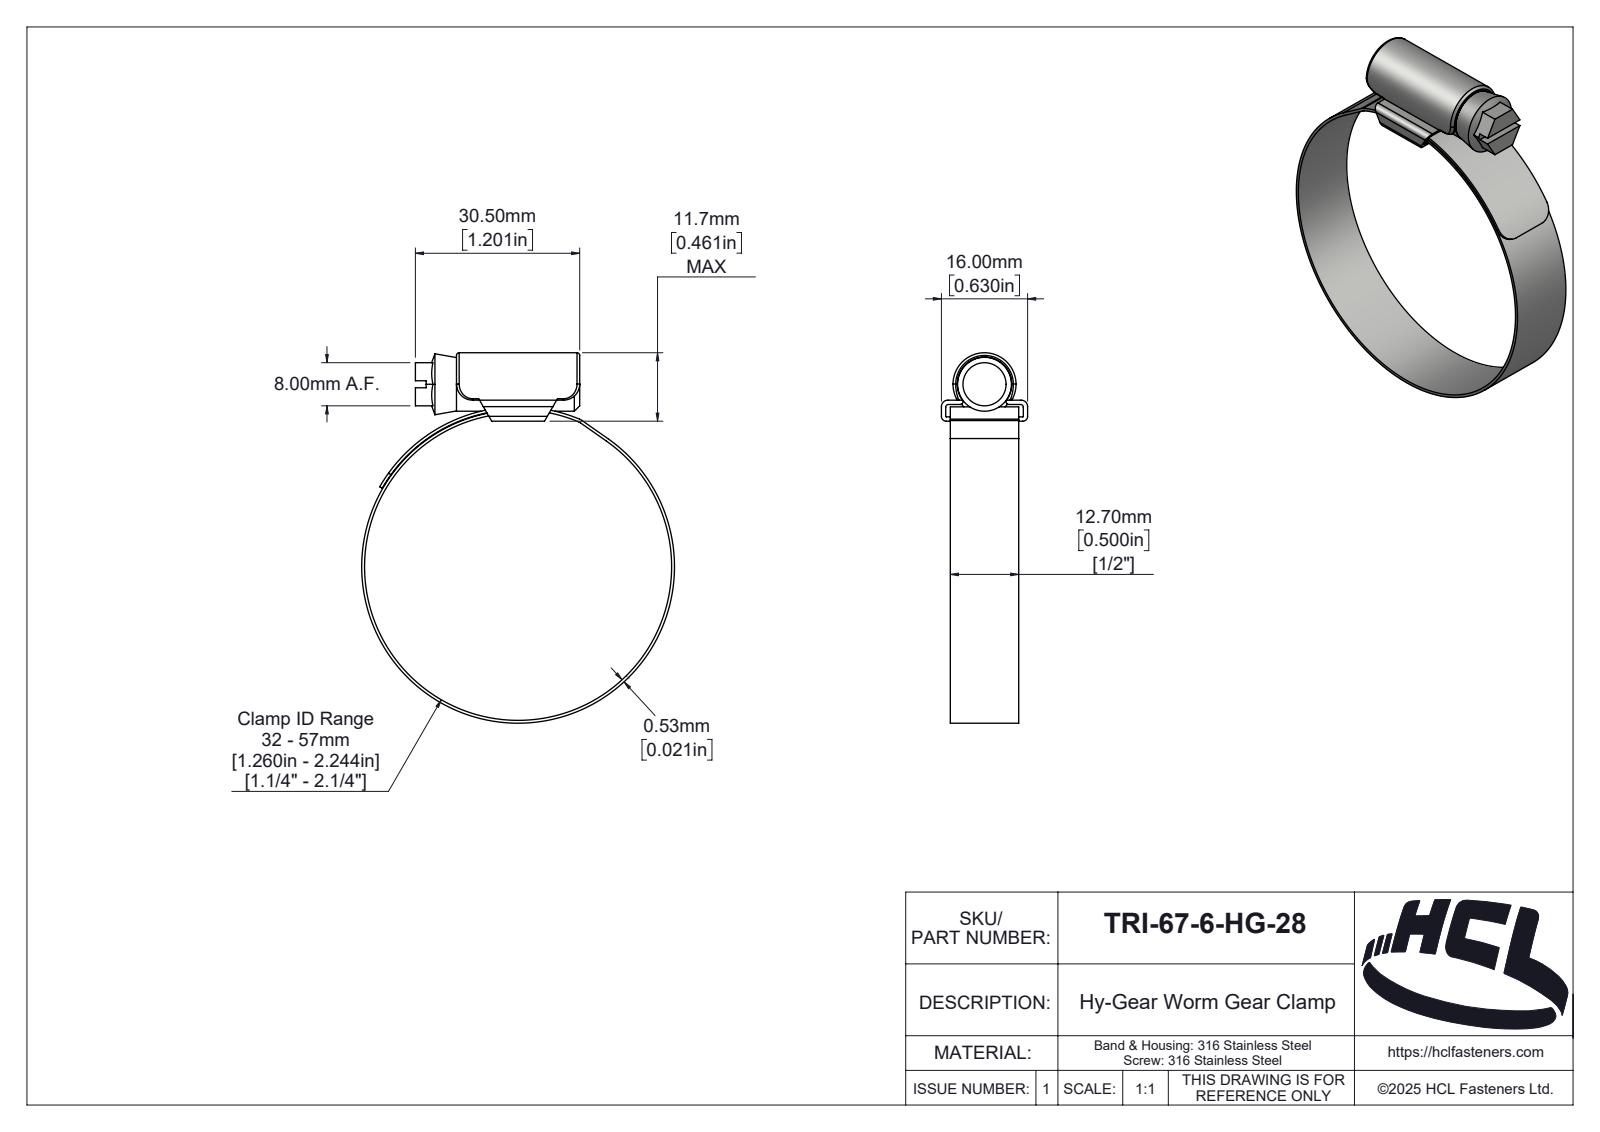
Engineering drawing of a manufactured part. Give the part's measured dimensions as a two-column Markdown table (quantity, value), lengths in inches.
| quantity | value |
| --- | --- |
| part name | TRI-57-0-HG-28 |
| STEP written by | SolidWorks 2025 (AUTOMOTIVE_DESIGN) |
| units | inches |
| bodies | 3 solids, 189 faces (39 planar, 89 cylindrical, 61 other) |
| overall size | 2.706 × 2.286 × 0.63 |
| volume | 0.27 in³ |
| surface area | 13.19 in² |
| round holes (diameter × count) | 2.244 × 1 |
| round bosses / shafts (diameter × count) | 2.286 × 1, 0.394 × 1 |
| partial cylindrical surfaces (radius × count) | 0.02 × 6, 0.118 × 4, 0.004 × 2, 0.035 × 2, 0.047 × 2, 0.018 × 1, 0.074 × 1, 0.079 × 1 |
| main face-to-face distances | 0.031, 0.122, 0.5, 0.091, 0.021, 0.154, 1.201, 0.065, 0.565, 0.598 |
